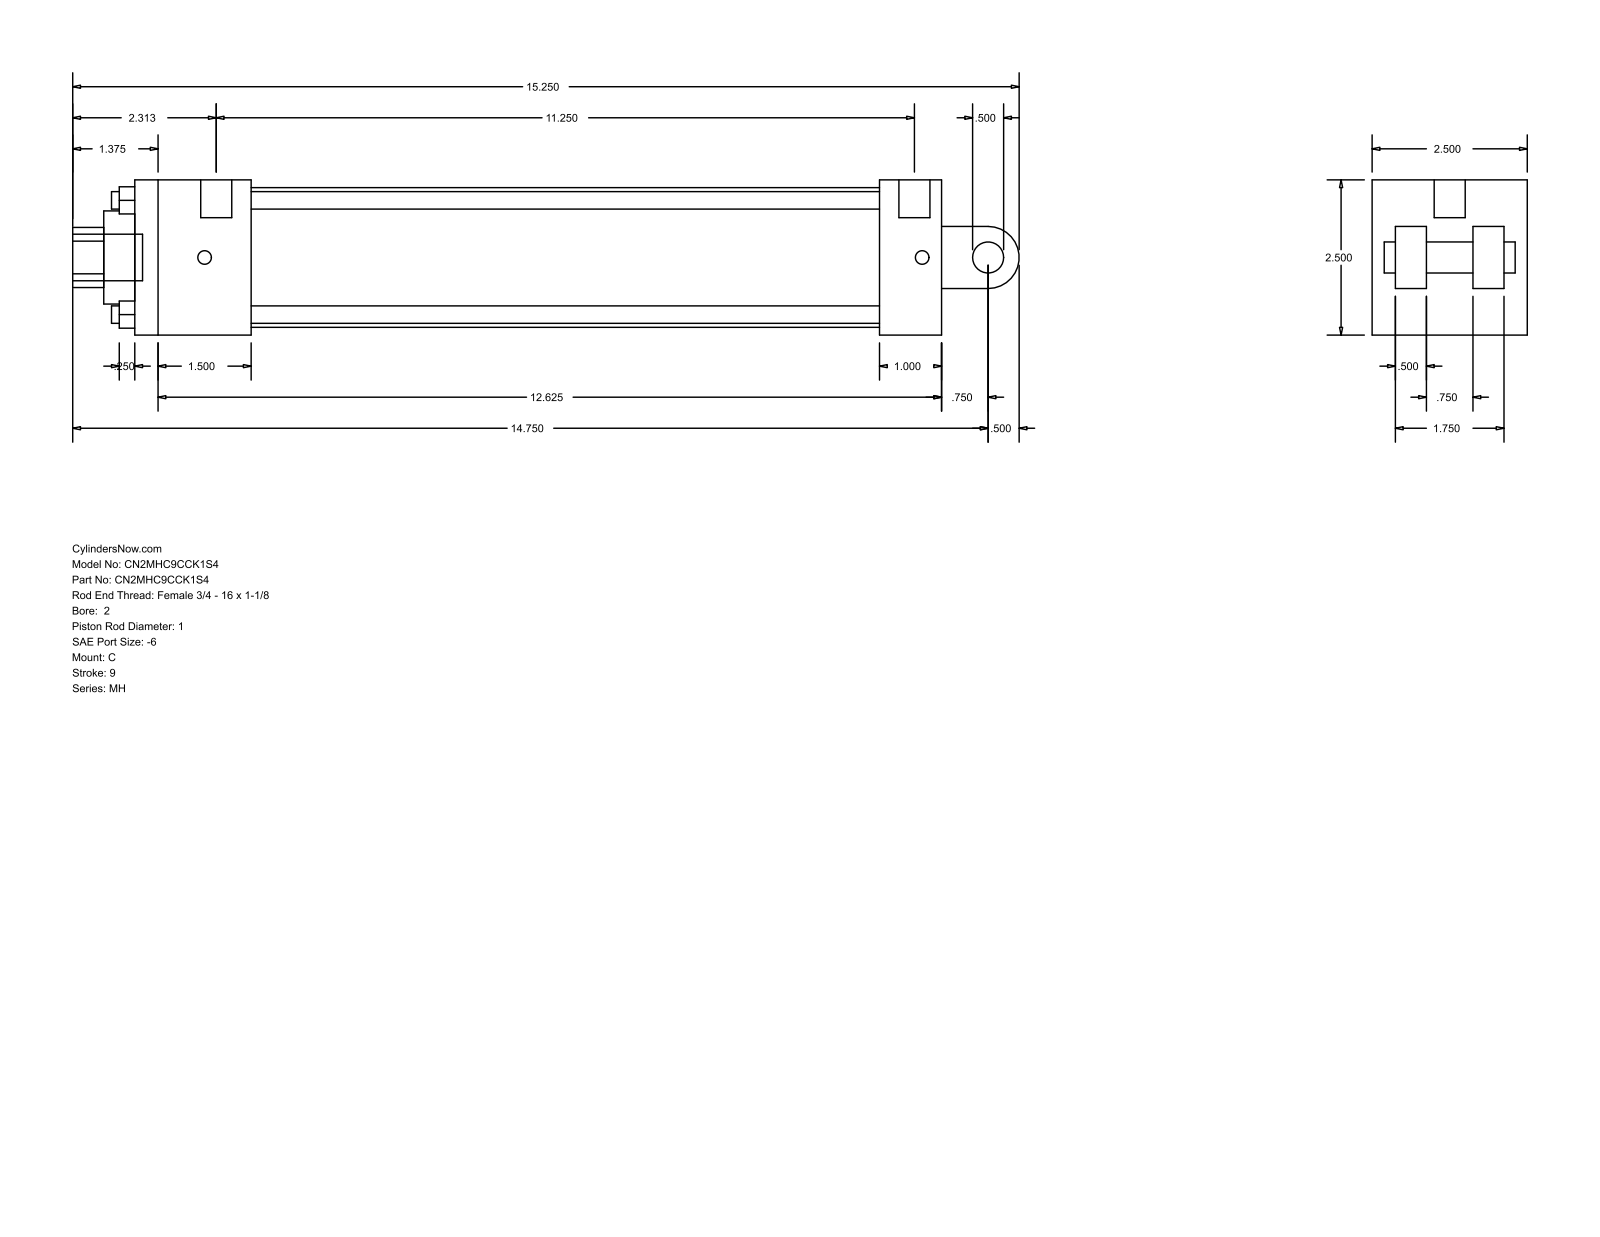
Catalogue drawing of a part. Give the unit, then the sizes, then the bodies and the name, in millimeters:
Units: millimetres
Overall size (bounding box): 387.35 × 63.5 × 63.5
Round holes (diameter × count): ⌀7.14 ×4, ⌀5.56 ×2, ⌀12.7 ×1, ⌀25.4 ×1, ⌀38.1 ×1, ⌀57.15 ×1
Round bosses / shafts (diameter × count): ⌀12.7 ×2, ⌀5.56 ×2, ⌀19.05 ×1
Partial cylindrical surfaces — rounded edges, fillets, slot ends (radius × count): R12.29 ×1, R12.7 ×1
Main face-to-face distances: 63.5, 330.2, 12.7, 25.4, 9.52, 47.63, 53.98, 304.8, 257.17, 282.57
Hole centre spacings: 33.05, 46.74, 66.1, 3.17
Bodies: 0 solids, 99 faces (70 planar, 29 cylindrical, 0 other)
Part name (STEP PRODUCT): MH_C__0200_1
STEP written by: GSSL Pune (CONFIG_CONTROL_DESIGN)
